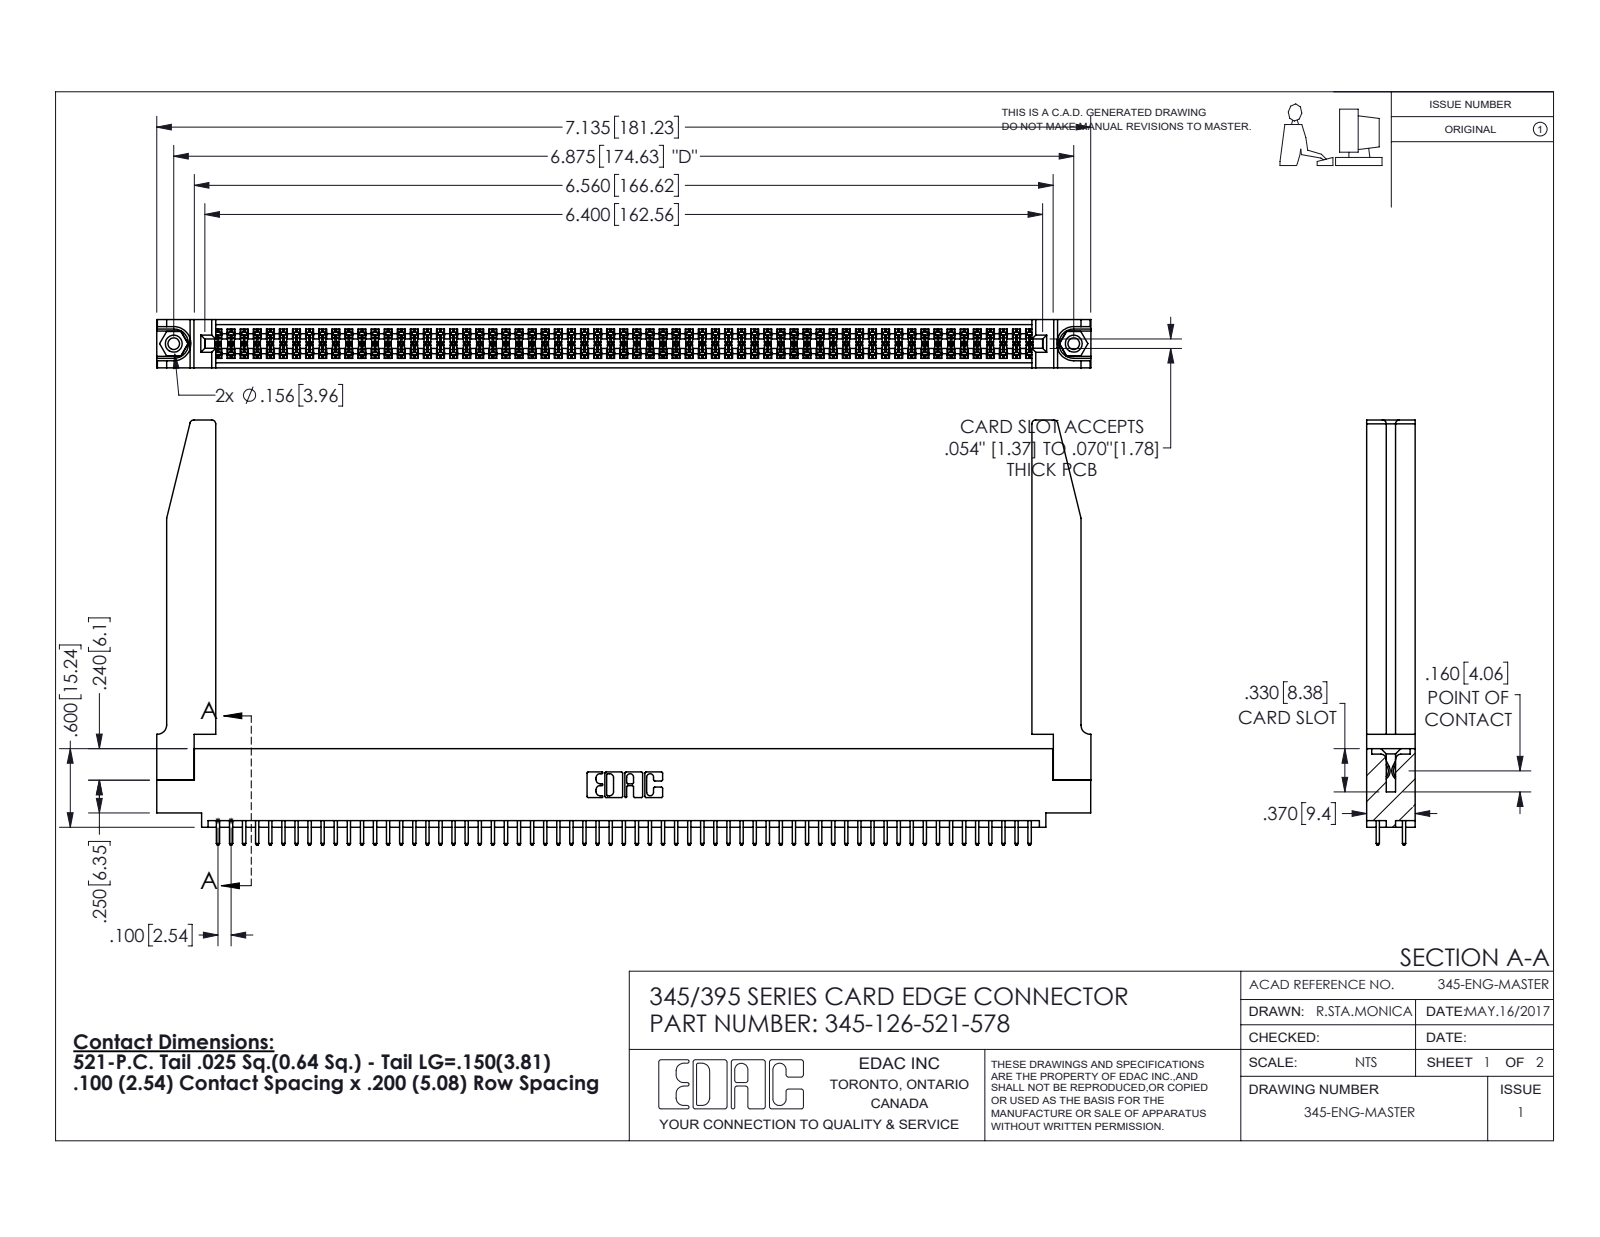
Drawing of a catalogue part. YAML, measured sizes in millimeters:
part_name: "345-220-078_345-220-078; 345 Part_0.110 Offset - 0.156 Dia-TH; 345-126-521-578; 345-250-001_345-250-001-102 (+1 more)"
step_written_by: "SolidWorks 2016 (CONFIG_CONTROL_DESIGN)"
units: millimeters
bodies: {solids: 131, faces: 6664, planar: 4384, cylindrical: 2228, other: 52}
overall_size: [181.3, 82.5, 9.4]
volume: 25450
surface_area: 33140
round_holes:
  - {diameter: 2.3, count: 2}
  - {diameter: 3.2, count: 2}
  - {diameter: 4, count: 2}
  - {diameter: 1.6, count: 1}
round_bosses_or_shafts:
  - {diameter: 3.9, count: 2}
partial_cylinders:
  - {radius: 0.2, count: 189}
  - {radius: 0.3, count: 126}
  - {radius: 0.3, count: 22}
  - {radius: 0.8, count: 8}
  - {radius: 0.2, count: 6}
  - {radius: 0.8, count: 6}
  - {radius: 0.7, count: 3}
  - {radius: 0.4, count: 2}
face_to_face_distances: [1.8, 7.6, 9.4, 5.1, 2.5, 6.9, 0.6, 5.7, 4.4, 3.8]
hole_center_spacings: [6.9, 168.6, 174.6]
